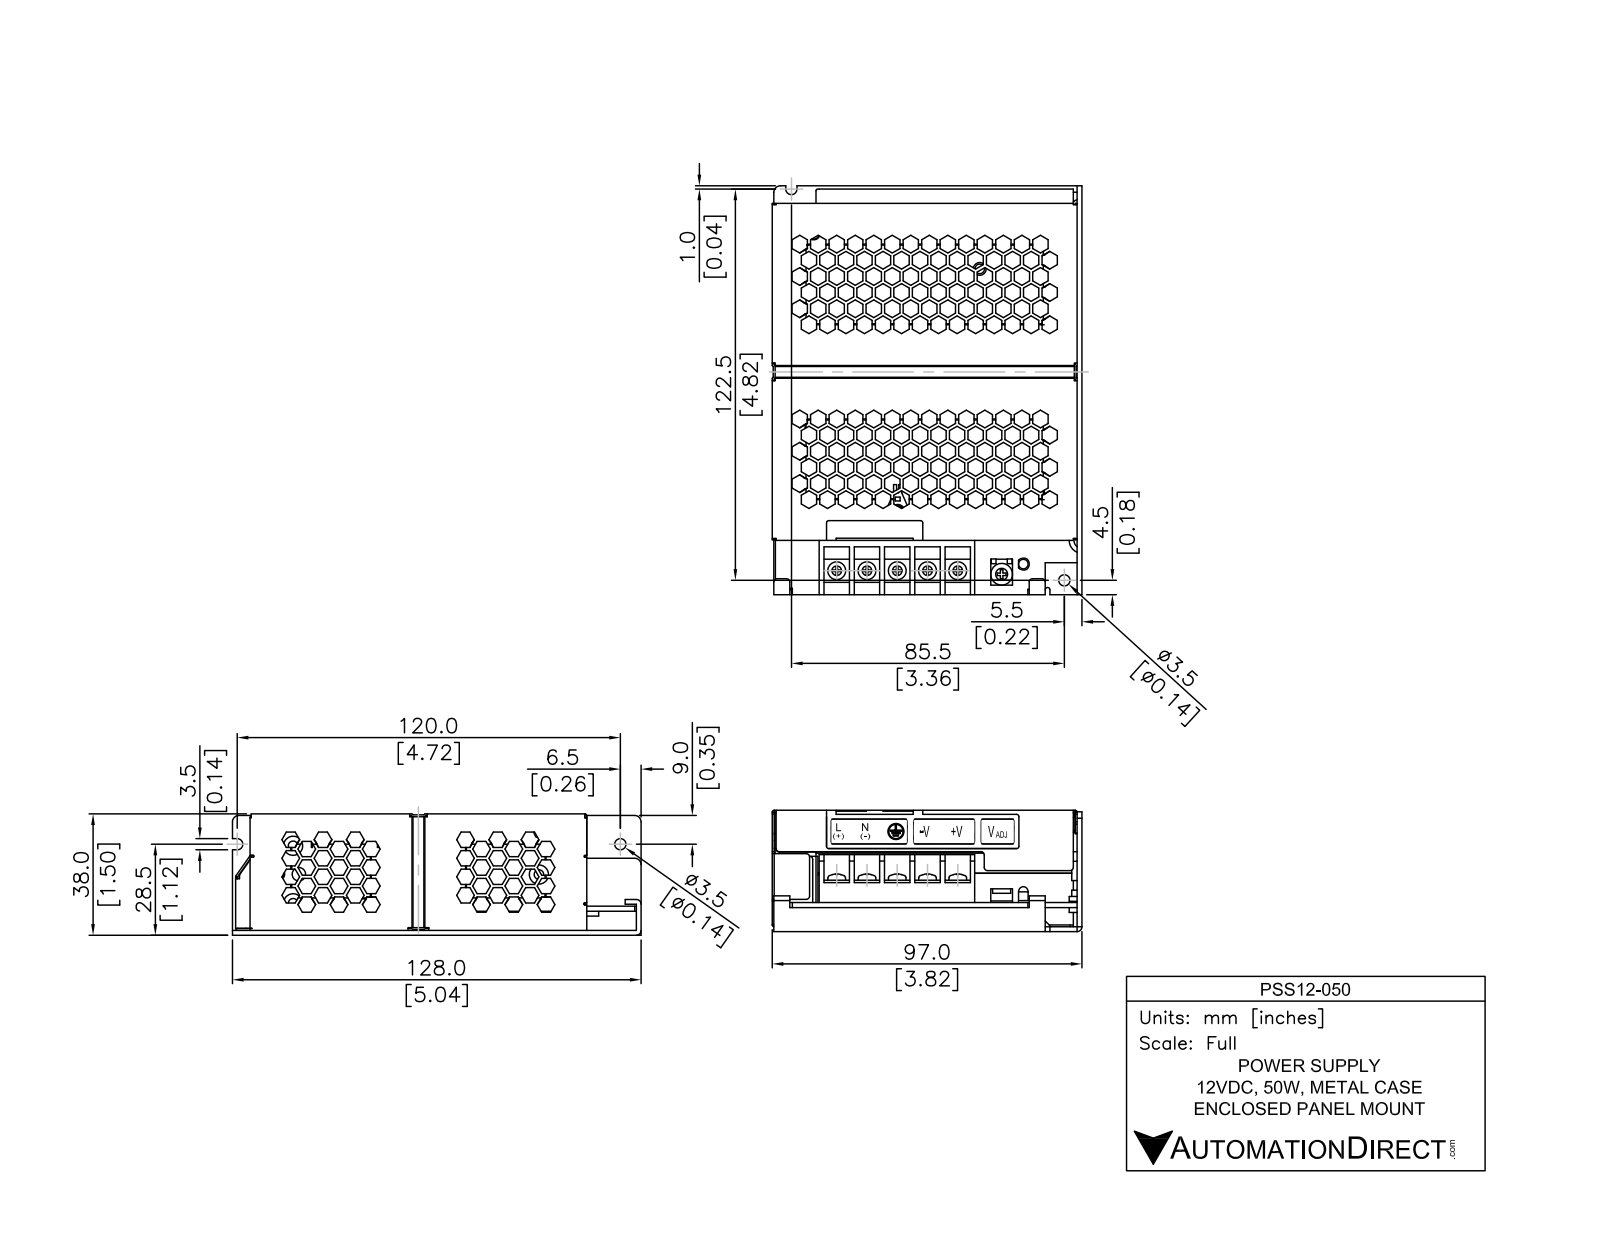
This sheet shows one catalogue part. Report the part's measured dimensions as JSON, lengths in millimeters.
{"part_name": "PSS 12-050", "step_written_by": "SolidWorks 2011 (CONFIG_CONTROL_DESIGN)", "units": "millimeters", "bodies": {"solids": 3, "faces": 1670, "planar": 1540, "cylindrical": 68, "other": 62}, "overall_size": [128, 97, 38.1], "volume_mm3": 164200, "surface_area_mm2": 100800, "round_holes": [[3.3, 2]], "round_bosses_or_shafts": [[5.6, 5], [0.7, 2], [7, 1], [3.1, 1], [1.8, 1], [1.7, 1]], "partial_cylinders_radius": [[0.8, 7], [1, 5], [1.3, 5], [1.5, 4], [0.4, 2], [1.8, 2], [4.4, 2], [2.5, 1]], "face_to_face_distances": [0.8, 37.3, 9.8, 27.6, 8.3, 36.6, 7.5, 1.5, 9, 28.3]}
